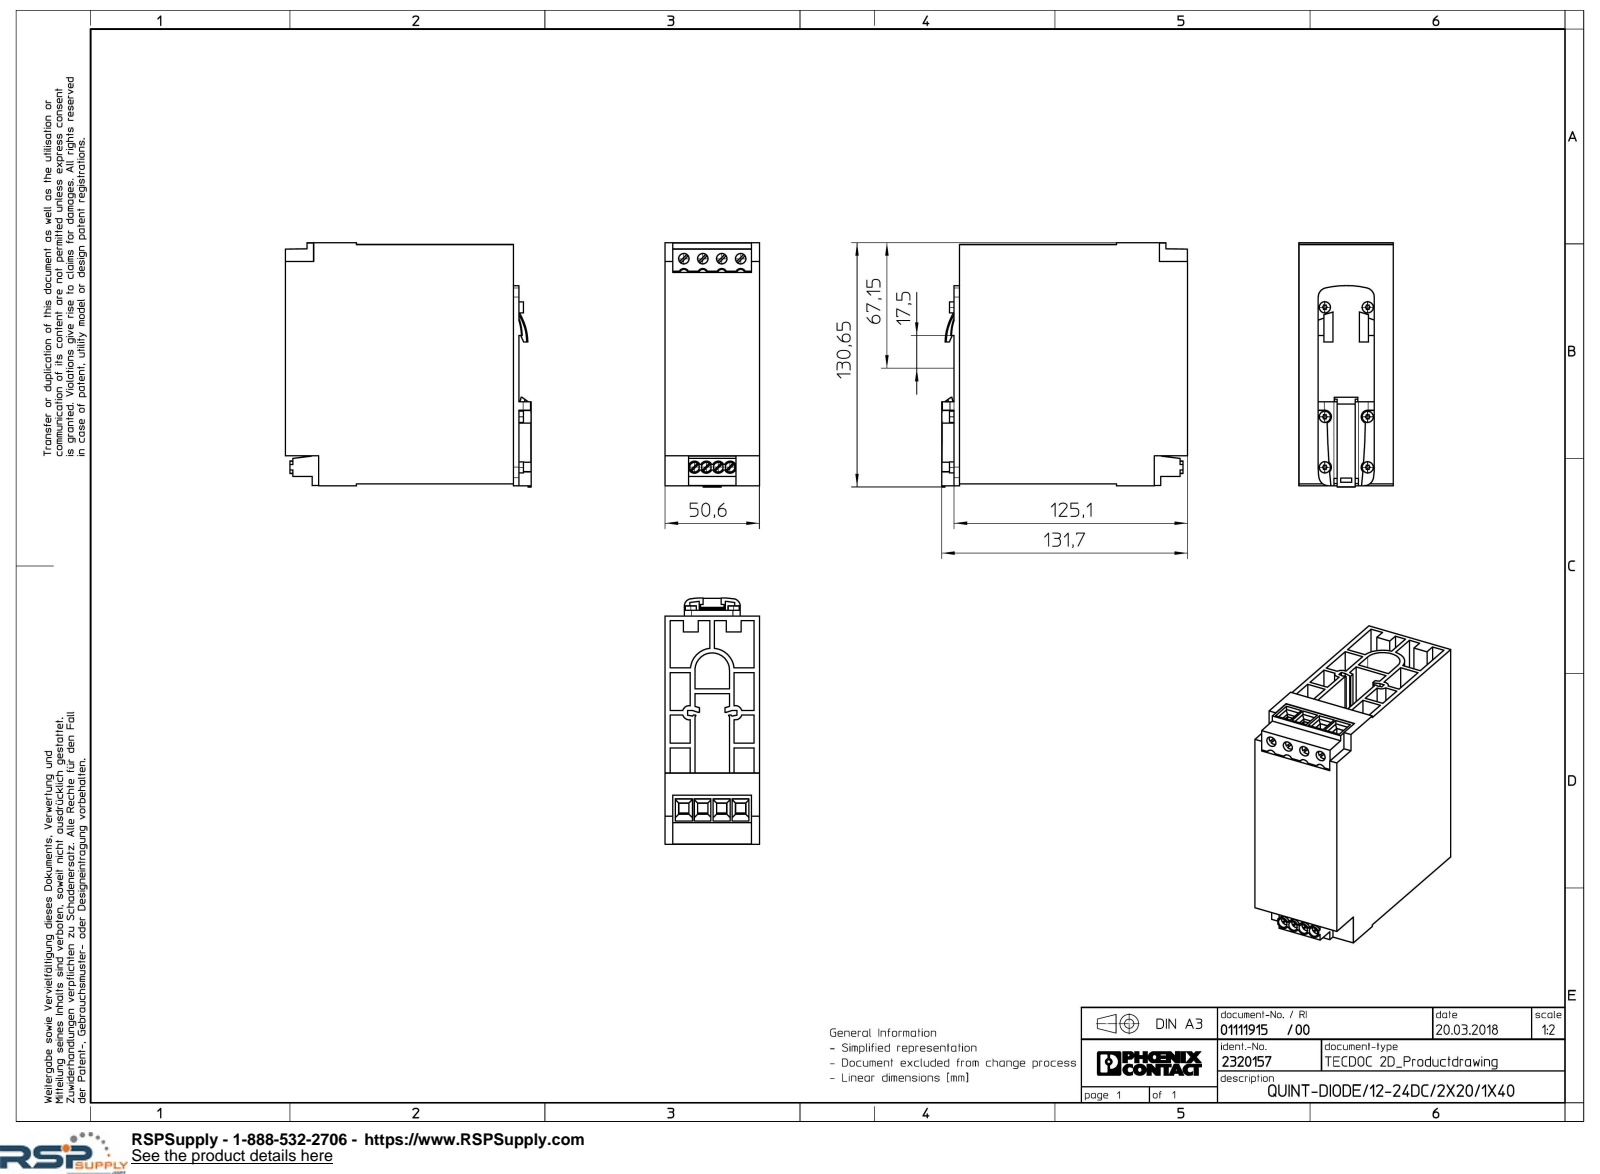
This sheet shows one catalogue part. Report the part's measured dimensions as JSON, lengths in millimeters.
{"part_name": "QUINT_DIODE_12_24DC_2X20_1X40-select", "step_written_by": "Creo Elements/Direct Modeling 18.1I 14-Aug-2016 (C) Parametric Technology GmbH (AUTOMOTIVE_DESIGN)", "units": "millimeters", "bodies": {"solids": 1, "faces": 502, "planar": 370, "cylindrical": 124, "other": 8}, "overall_size": [131.7, 130.65, 50.6], "volume_mm3": 415502, "surface_area_mm2": 151624, "round_holes": [[5.2, 4], [5.6, 4]], "round_bosses_or_shafts": [[6, 6]], "partial_cylinders_radius": [[1.3, 36], [2.7, 16], [3.5, 8], [3.25, 5], [0.5, 4], [2.75, 4], [5, 4], [0.25, 2]], "face_to_face_distances": [2.5, 2.8, 47.8, 50.6, 16.05, 34.55, 13.25, 31.75, 45, 13.55], "hole_center_spacings": [10.16, 6.35, 20.32, 111.45, 111.52, 111.58, 112.08, 112.38]}
